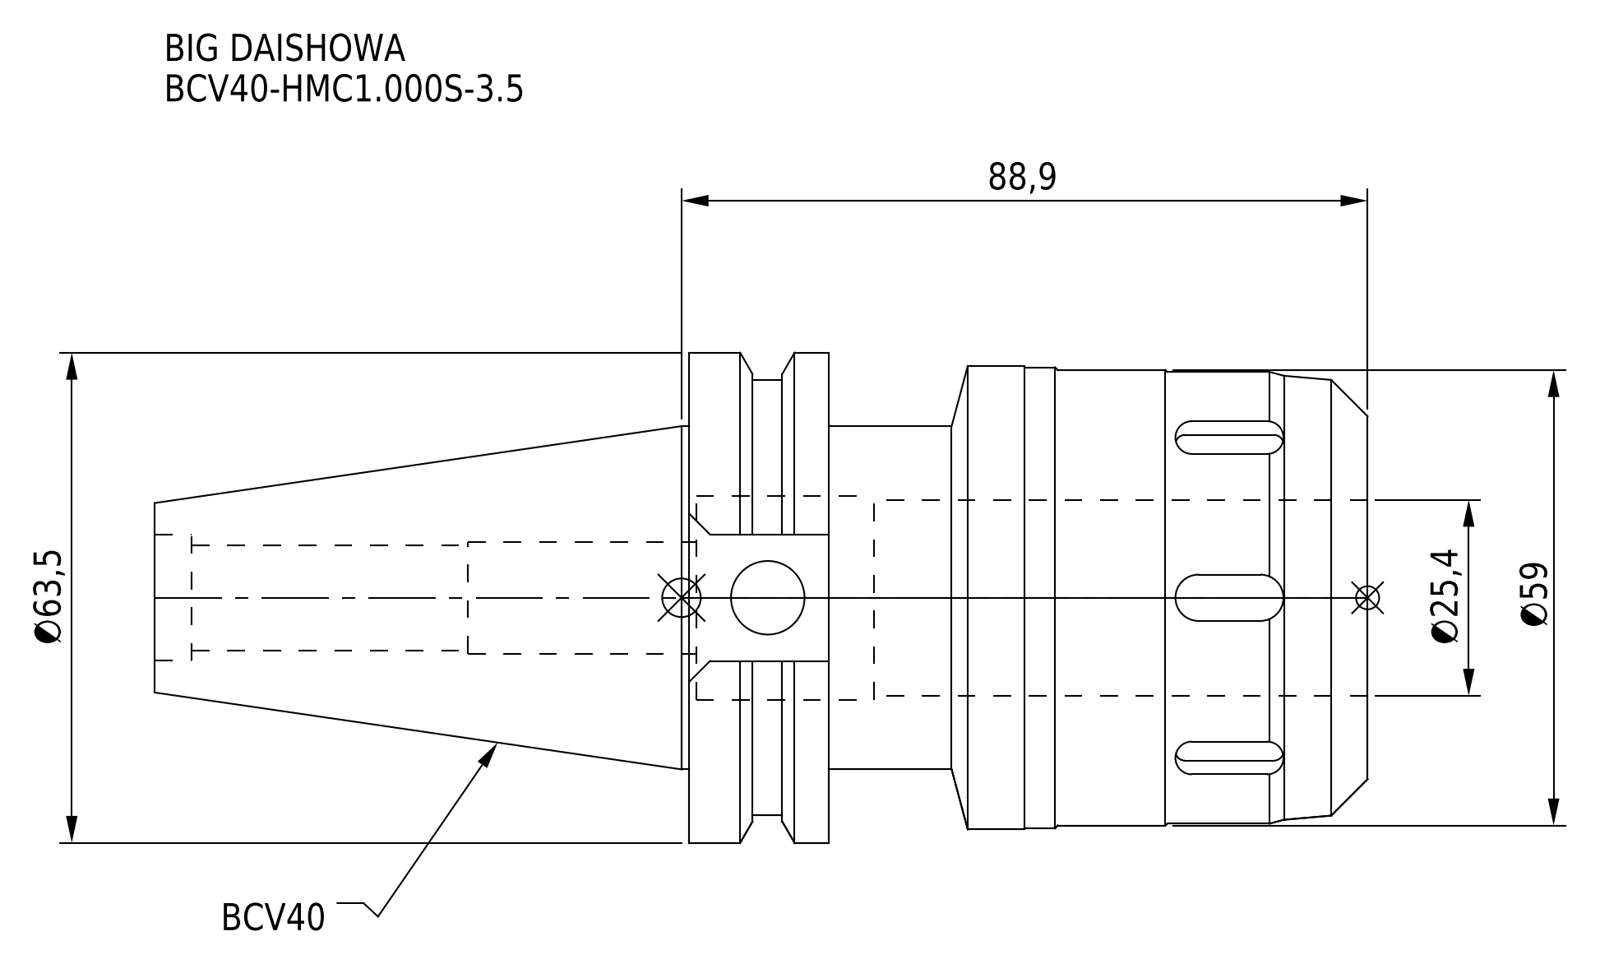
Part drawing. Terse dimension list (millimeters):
name: BCV40-HMC1_000S-3_5
written by: CREO PARAMETRIC BY PTC INC, 2016380 (AUTOMOTIVE_DESIGN)
unit: mm
bodies: 1 solid, 114 faces (48 planar, 48 cylindrical, 18 other)
size: 157.15 × 63.5 × 61.35
volume: 226 348 mm³; area: 41 079 mm²
holes: 1× ⌀9.53, 1× ⌀13.6, 1× ⌀14.5, 1× ⌀16.32, 1× ⌀25.4, 1× ⌀26.4
bosses: 1× ⌀63.5, 1× ⌀60, 1× ⌀59.7, 1× ⌀59, 1× ⌀58.5, 1× ⌀56.36, 1× ⌀44.45
rounds: 12× R3
face distances: 18.05, 69.85, 87.9, 87, 17.15, 0.9, 54, 24, 30, 157.15
